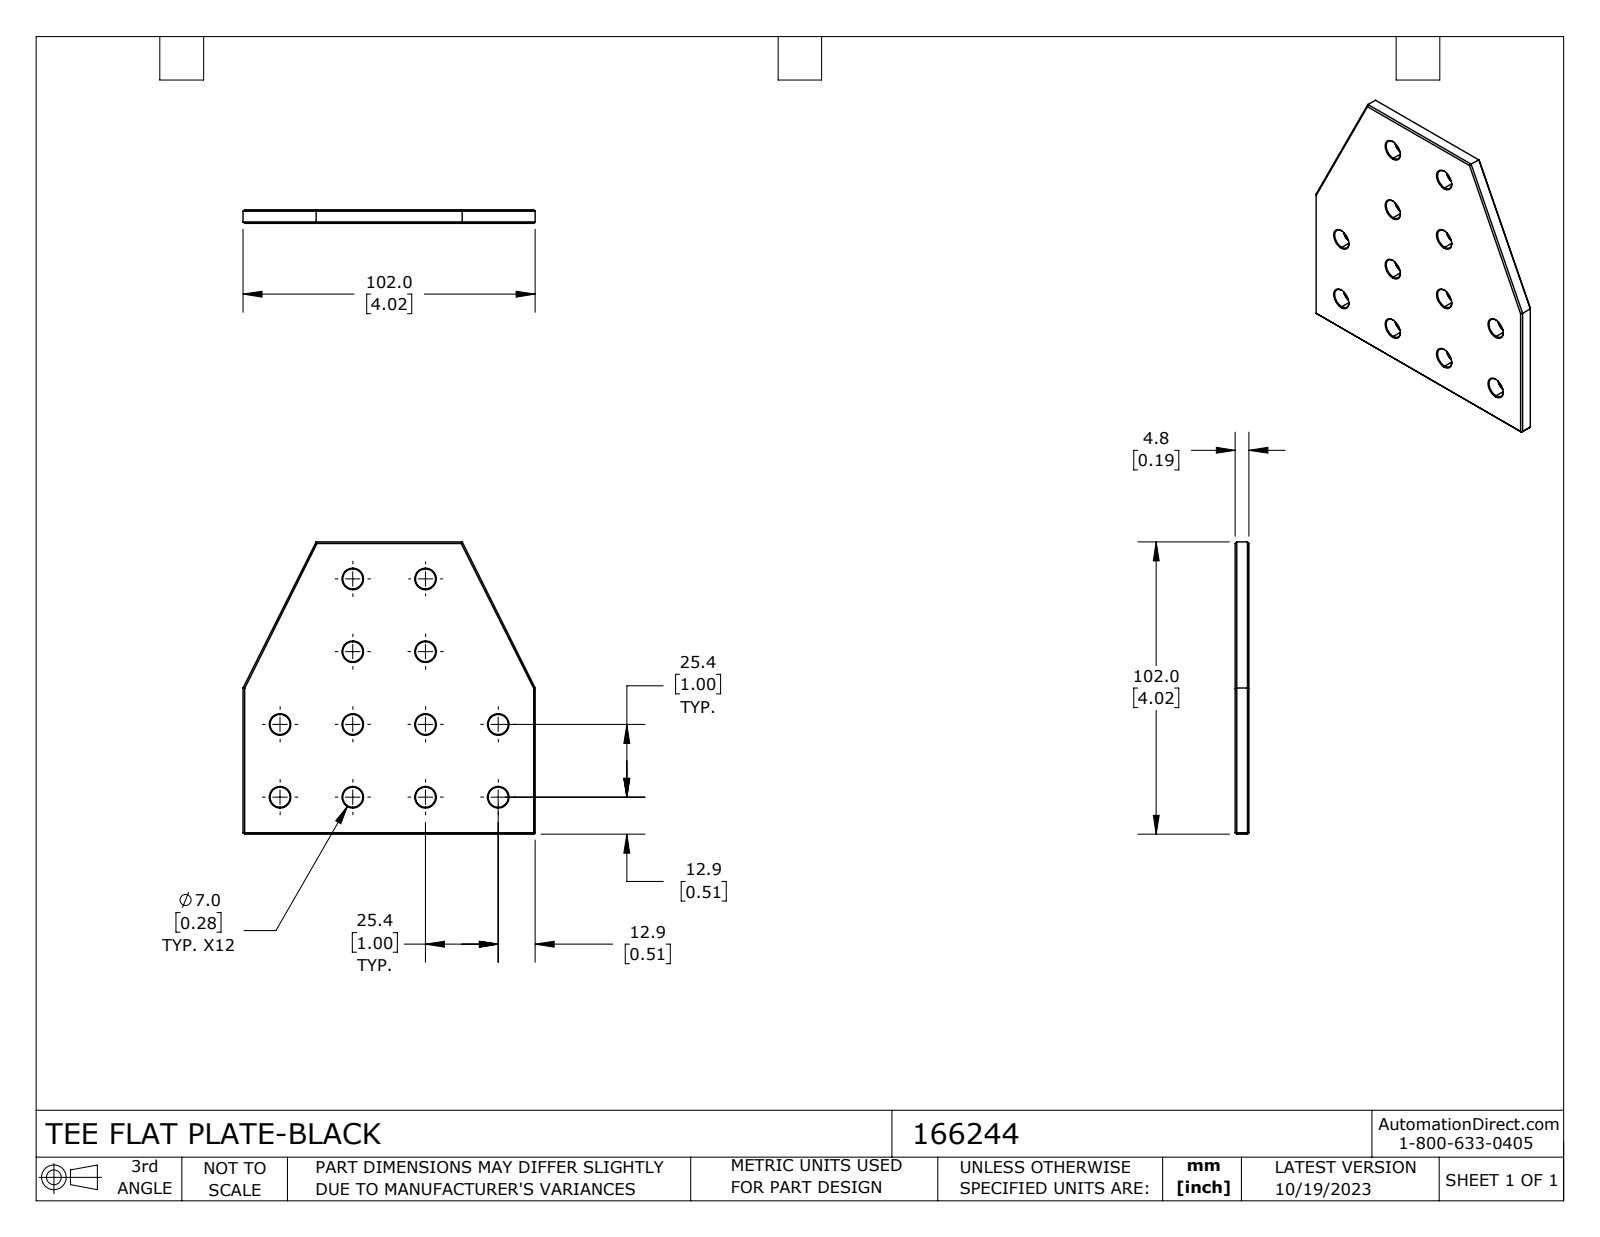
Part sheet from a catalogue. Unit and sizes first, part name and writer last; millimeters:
Units: millimetres
Overall size (bounding box): 102 × 102 × 4.76
Round holes (diameter × count): ⌀7 ×12
Main face-to-face distances: 4.76, 102, 74.77
Hole centre spacings: 25.4, 56.8, 35.92, 50.8, 80.32, 71.84, 76.2, 91.58
Volume: 41 046 mm³ · Surface area: 20 003 mm²
Bodies: 1 solid, 98 faces (26 planar, 24 cylindrical, 48 other)
Part name (STEP PRODUCT): 166244
STEP written by: SolidWorks 2023 (CONFIG_CONTROL_DESIGN)
